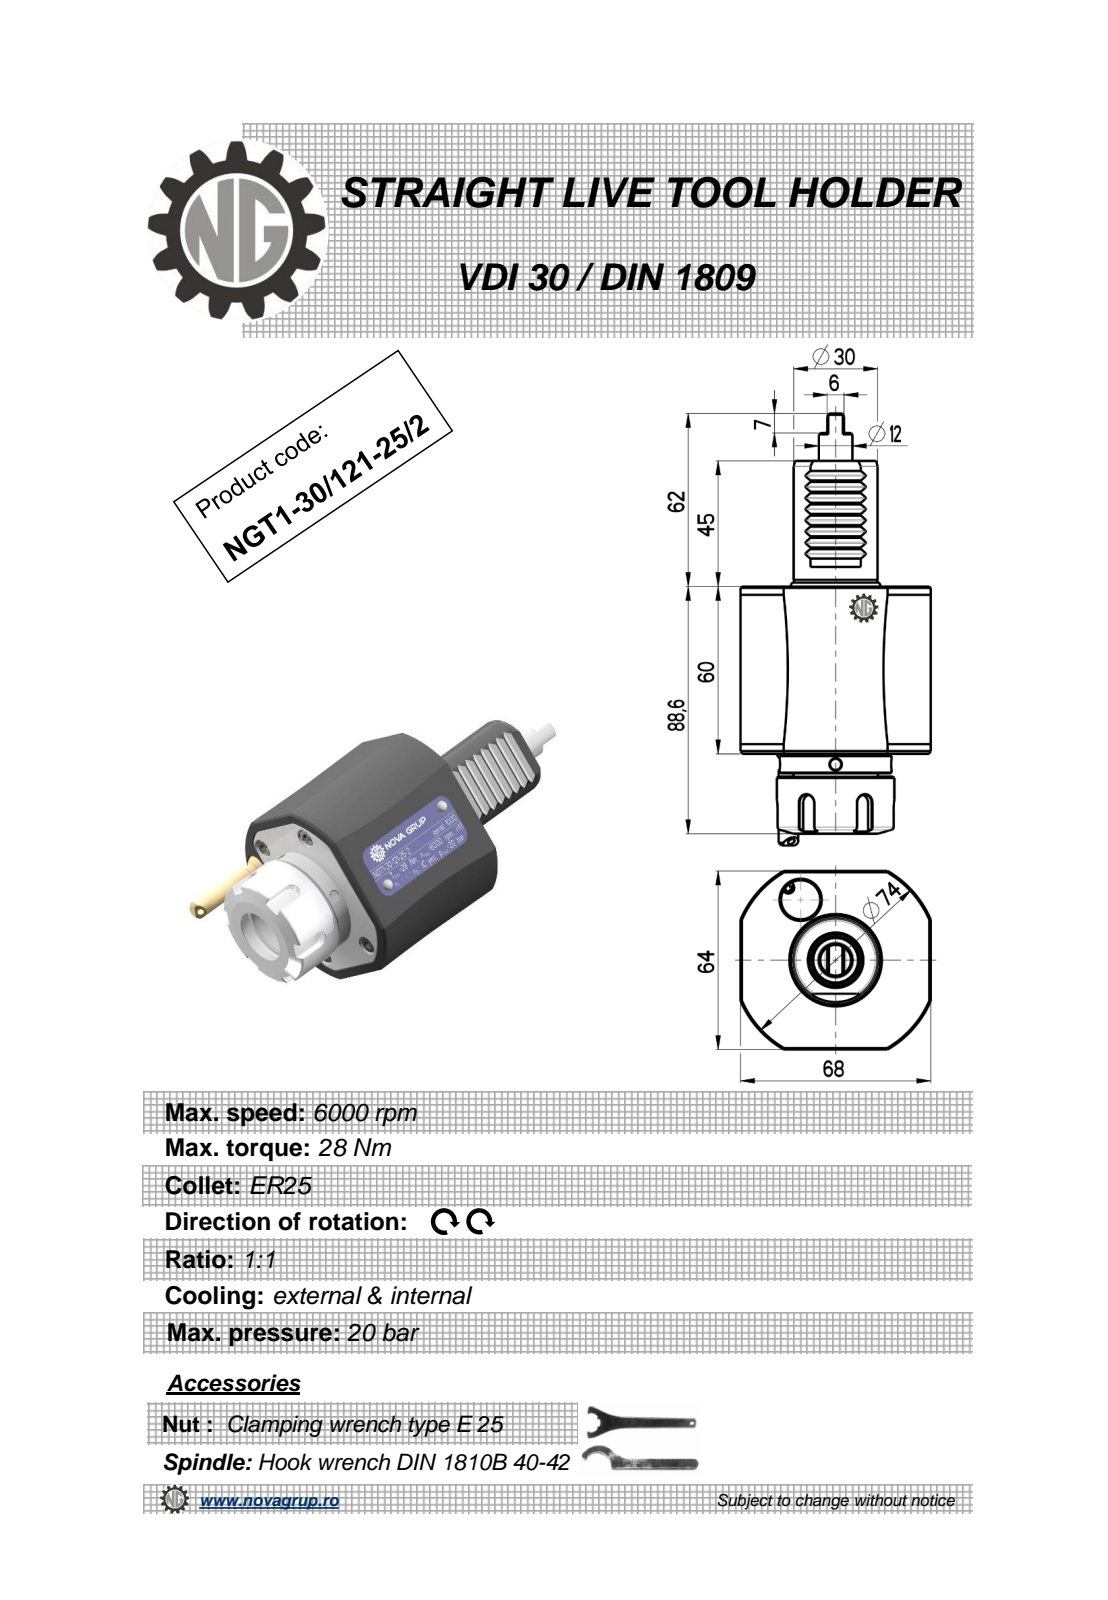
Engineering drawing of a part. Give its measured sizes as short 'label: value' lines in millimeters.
name: NGT1_30_121_25_1
written by: PRO/ENGINEER BY PARAMETRIC TECHNOLOGY CORPORATION, 2010280 (CONFIG_CONTROL_DESIGN)
unit: mm
bodies: 1 solid, 255 faces (98 planar, 64 cylindrical, 93 other)
size: 154.83 × 68 × 65.6
volume: 298 672 mm³; area: 34 064 mm²
holes: 2× ⌀4, 1× ⌀2.5, 1× ⌀3, 1× ⌀20.3, 1× ⌀25.8
bosses: 1× ⌀42, 1× ⌀40, 1× ⌀33, 1× ⌀30, 1× ⌀12, 1× ⌀9, 1× ⌀7, 1× ⌀5
rounds: 8× R0.3, 5× R3, 2× R0.8, 1× R13.9, 1× R37
face distances: 60, 64, 68, 81.7, 21.7, 2.83, 45, 105, 126.7, 113.1
hole spacings: 1.5, 29.75, 31
